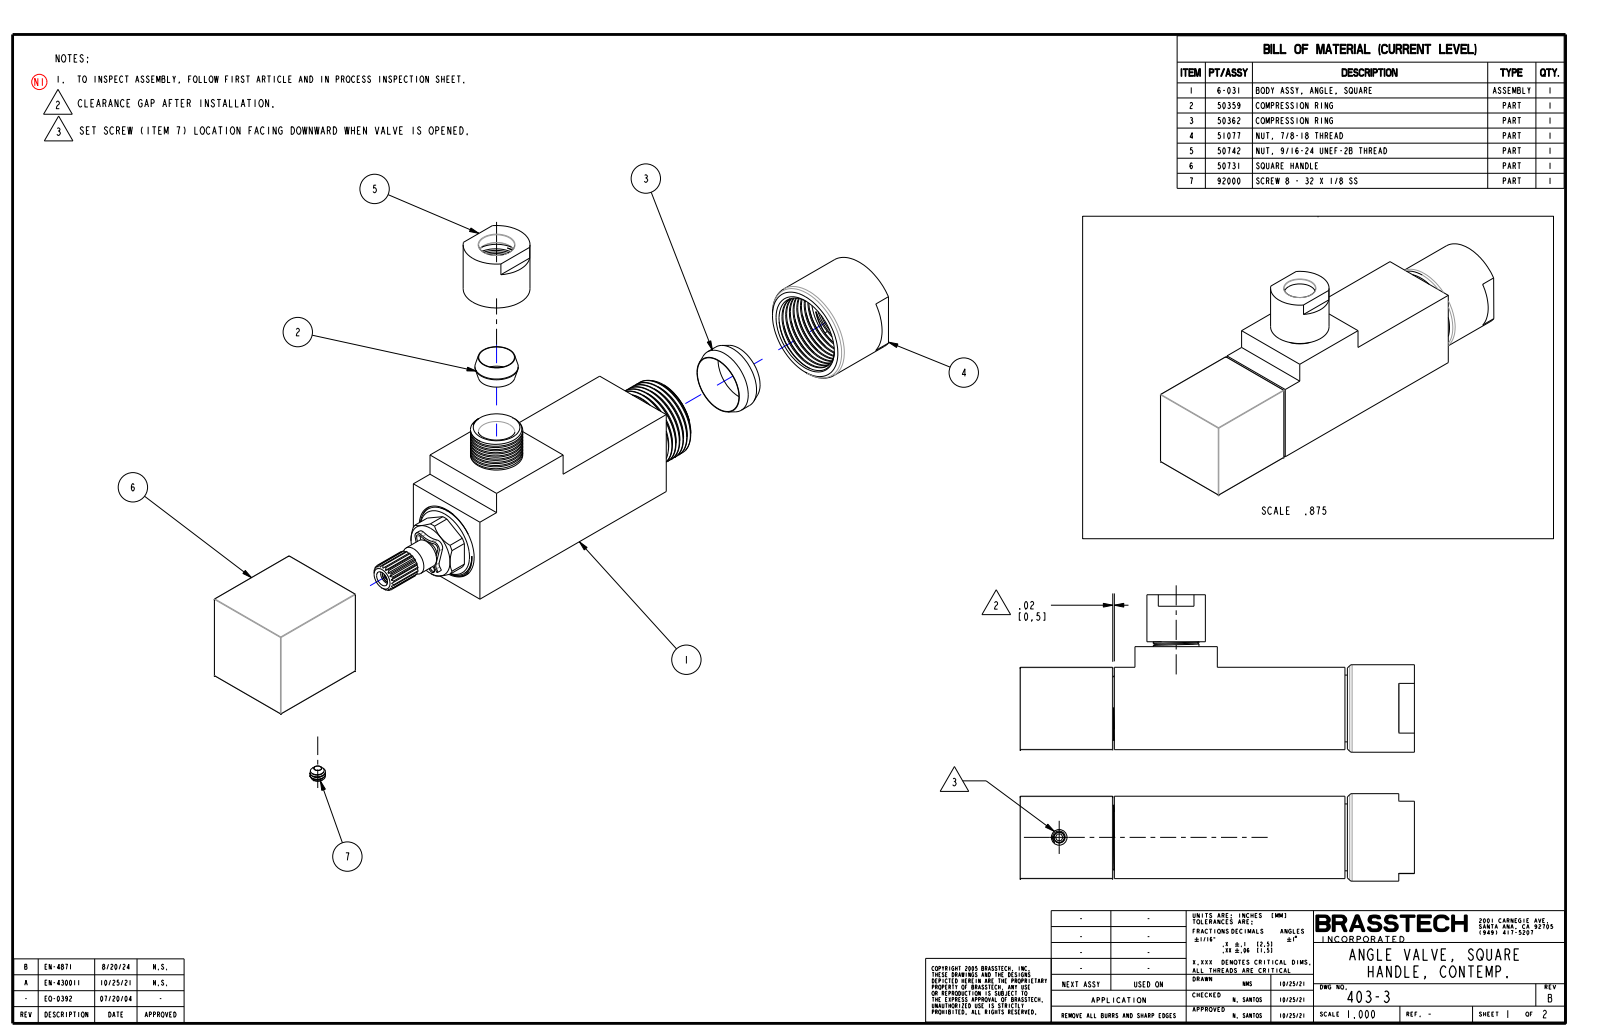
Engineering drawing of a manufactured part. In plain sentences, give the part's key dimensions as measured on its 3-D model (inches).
The part is named "403-3". Its 3-D file was written by "CREO PARAMETRIC BY PTC INC, 2018500 (CONFIG_CONTROL_DESIGN)". It is 2 solids with 567 faces: 144 planar, 260 cylindrical and 163 other. Overall it measures 4.839 by 1.88 by 1 inches. Its volume is 2.499 cubic inches and its surface area 75.26 square inches. Round holes: 1 of diameter 0.13, 1 of diameter 0.272, 1 of diameter 0.275, 1 of diameter 0.3, 1 of diameter 0.33, 1 of diameter 0.38, 1 of diameter 0.382, 1 of diameter 0.387, 1 of diameter 0.527, 1 of diameter 0.6, 1 of diameter 0.625, 1 of diameter 0.634. Round bosses or shafts: 1 of diameter 0.893, 1 of diameter 0.885, 1 of diameter 0.828, 1 of diameter 0.734, 1 of diameter 0.717, 1 of diameter 0.555, 1 of diameter 0.46, 1 of diameter 0.164. Partial cylindrical surfaces (rounded edges, fillets, slot ends): 14 of radius 0.005, 1 of radius 0.082. The main face-to-face distances are 1, 4.839, 0.25, 1.25, 1.4, 2.294, 3.714, 1.125, 2.545, 1.42. The hole center spacings are 0.043, 1.377, 1.42.
